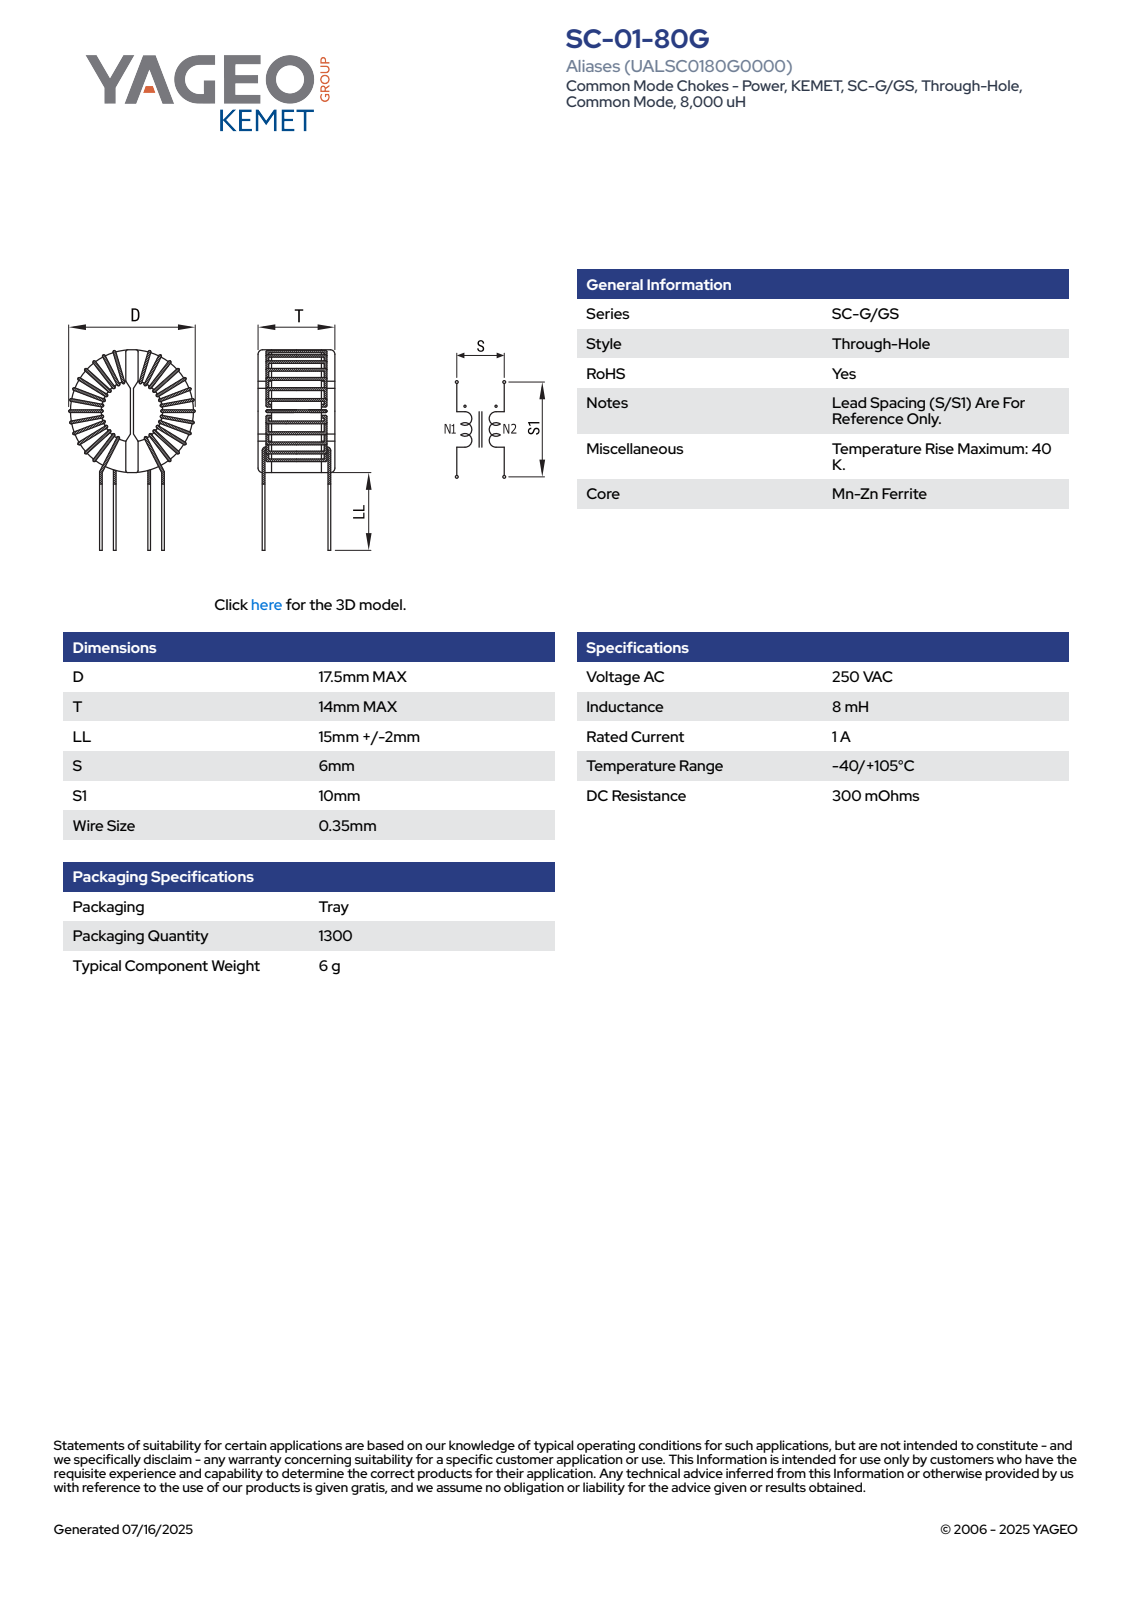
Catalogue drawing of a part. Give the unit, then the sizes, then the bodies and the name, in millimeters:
Units: millimetres
Overall size (bounding box): 30.38 × 17.5 × 14
Round bosses / shafts (diameter × count): ⌀0.35 ×8
Partial cylindrical surfaces — rounded edges, fillets, slot ends (radius × count): R0.17 ×16, R2.32 ×1, R3.21 ×1, R3.62 ×1, R3.67 ×1, R3.8 ×1, R6.35 ×1, R6.4 ×1
Main face-to-face distances: 1.2, 2, 8.3, 0.8, 3.2, 2.85, 11.15, 1.15, 2.05, 0.85
Volume: 1 783 mm³ · Surface area: 1 699 mm²
Bodies: 1 solid, 272 faces (121 planar, 73 cylindrical, 78 other)
Part name (STEP PRODUCT): SC-01-80G
STEP written by: SolidWorks 2018 (AUTOMOTIVE_DESIGN)
